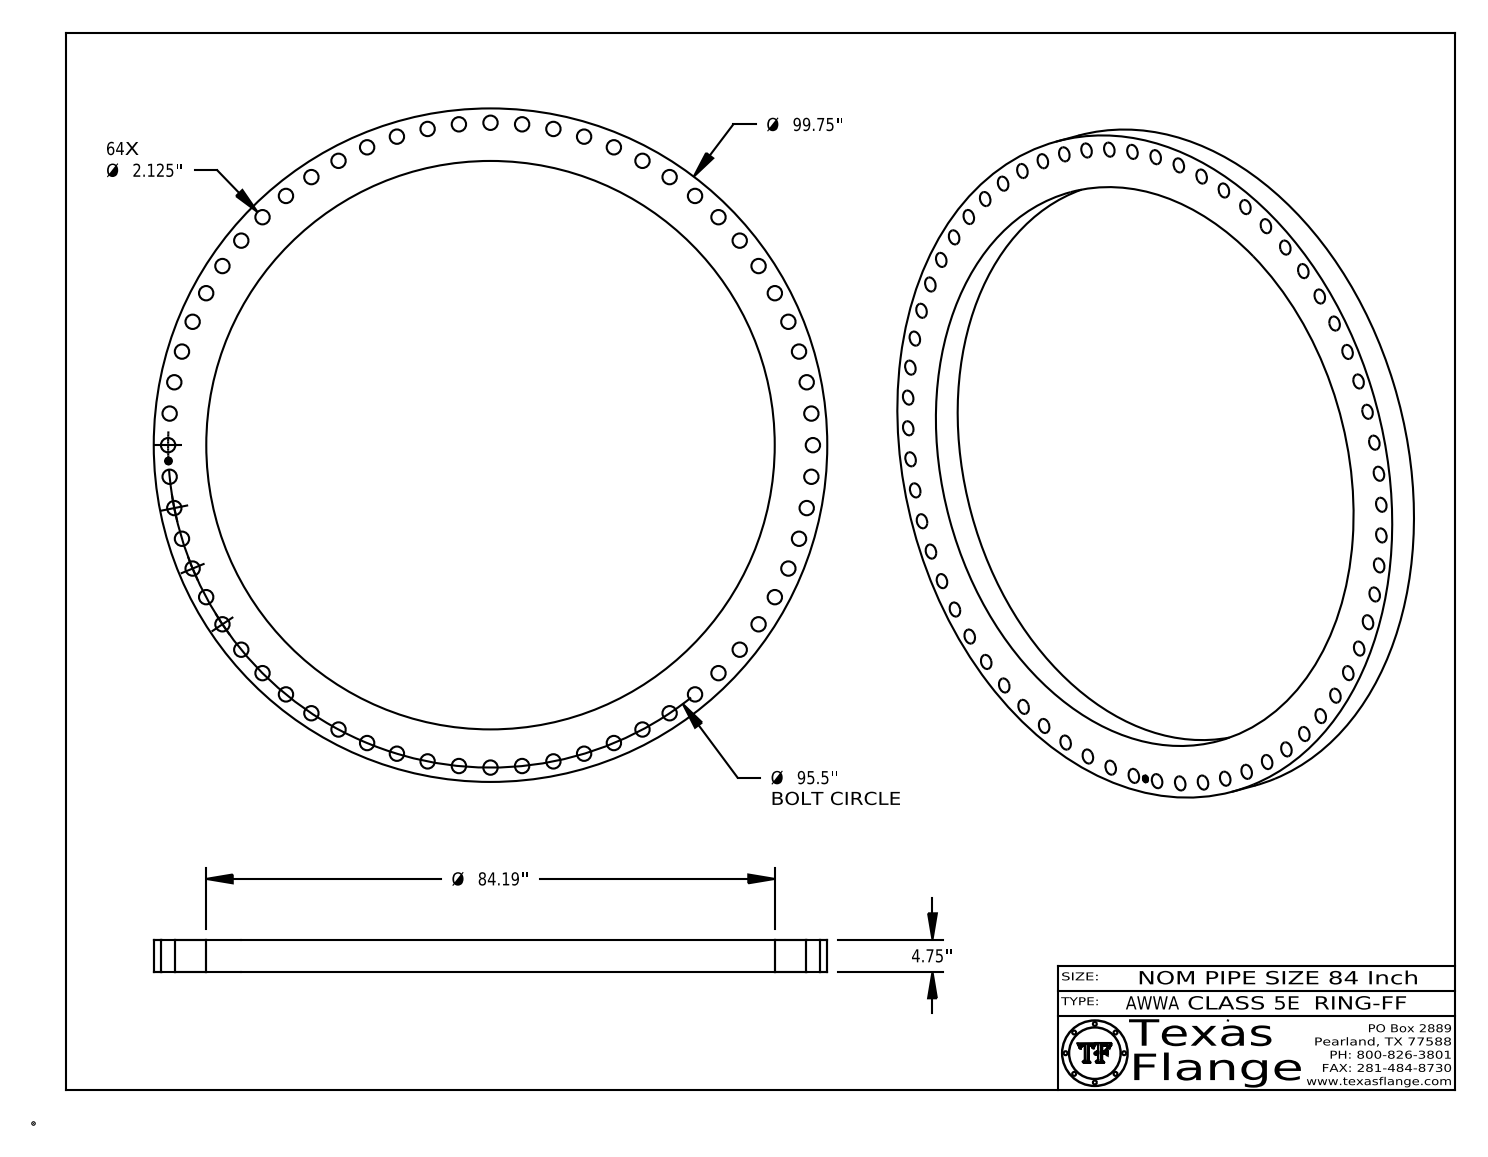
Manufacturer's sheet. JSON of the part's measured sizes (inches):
{"part_name": "AWWA Class 5E-RING-FF", "step_written_by": "CATIA V5 STEP AP214 (AUTOMOTIVE_DESIGN)", "units": "inches", "bodies": {"solids": 1, "faces": 519, "planar": 367, "cylindrical": 152, "other": 0}, "overall_size": [99.75, 99.75, 4.75], "volume_in3": 9599, "surface_area_in2": 8816, "round_holes": [[2.125, 64], [1, 1], [84.19, 1]], "round_bosses_or_shafts": [[0.061, 8], [99.75, 1], [0.788, 1]], "face_to_face_distances": [4.75, 0.015, 4.735, 0.298, 0.293, 0.055, 0.193, 0.248, 0.044, 0.15], "hole_center_spacings": [9.361, 47.75, 4.686, 18.631, 23.205, 45.019, 36.546, 40.831]}
